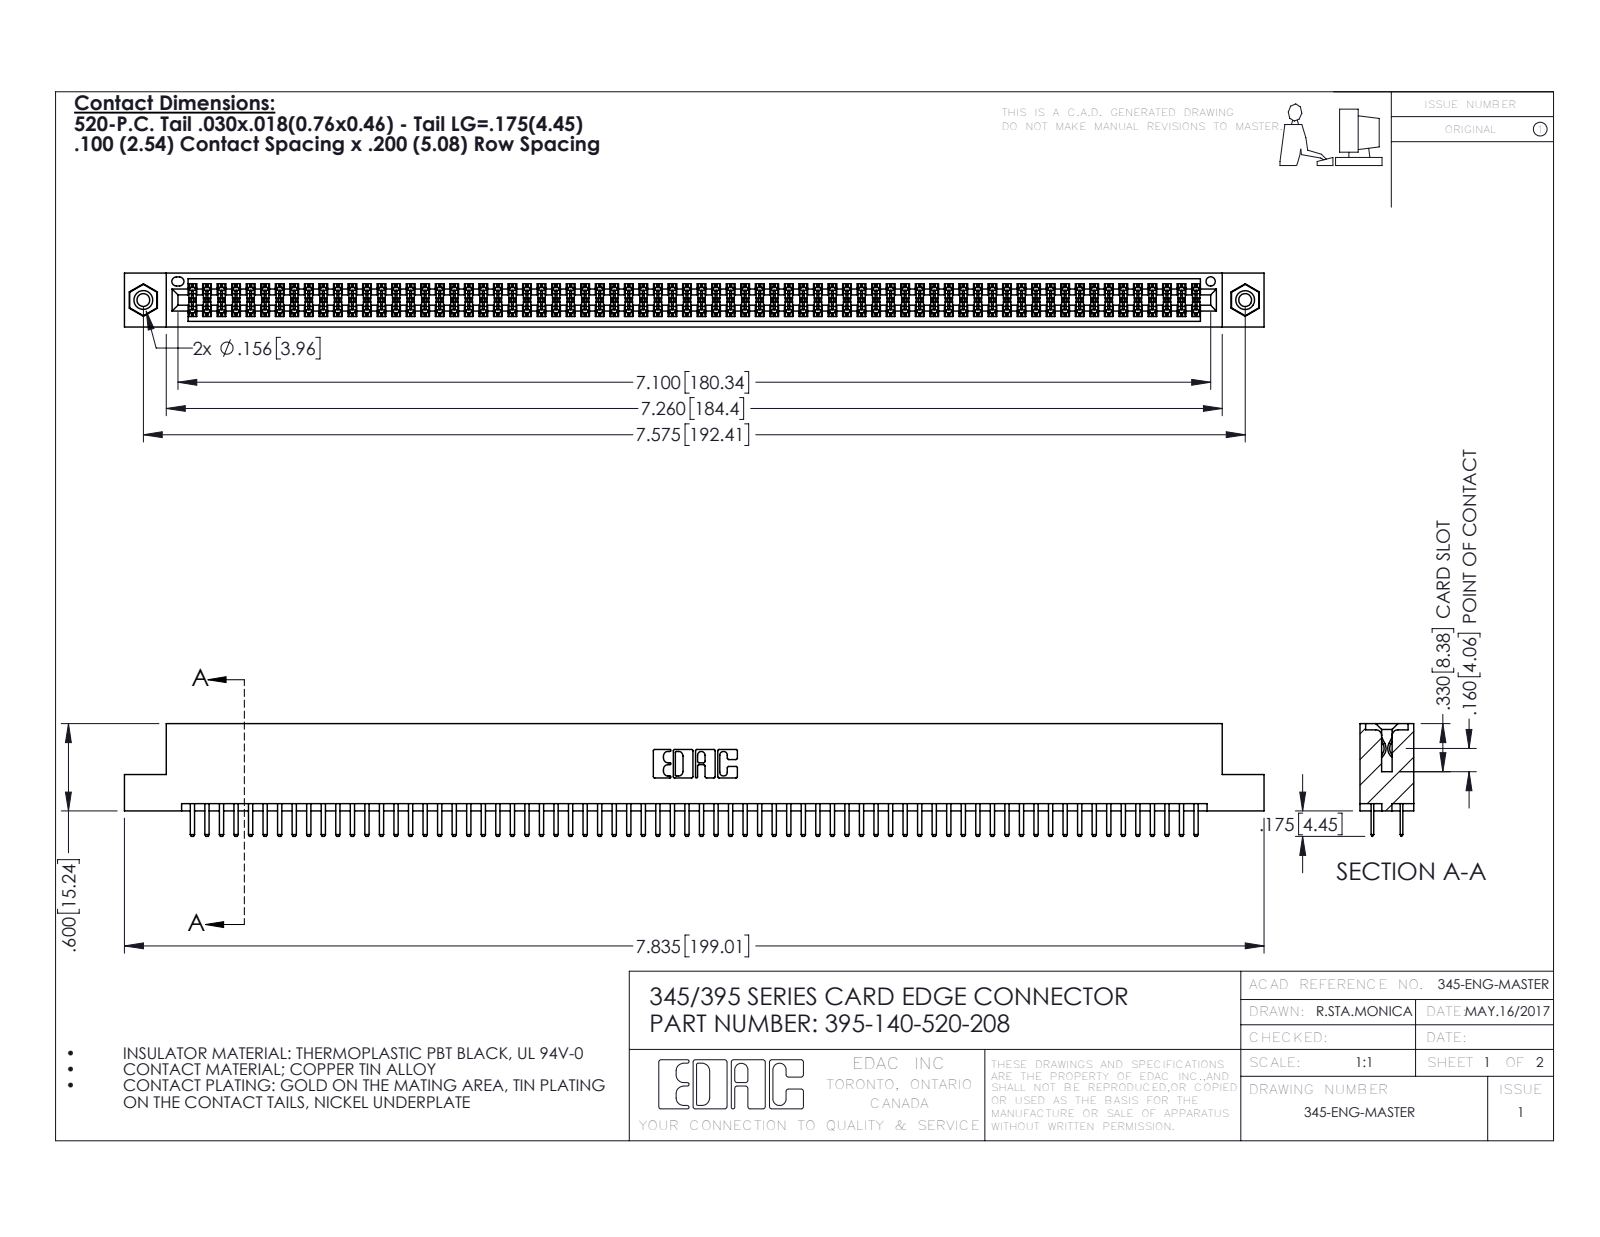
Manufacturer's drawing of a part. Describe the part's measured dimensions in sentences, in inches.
The part is named "395-140-520-208; 345-292-001_345-293-120; 345-250-001_345-250-003-102; 345 Part_Flush Mounting Lugs - 0.156 Dia-TI". Its 3-D file was written by "SolidWorks 2016 (CONFIG_CONTROL_DESIGN)". It is 143 solids with 7746 faces: 5012 planar, 2718 cylindrical and 16 other. Overall it measures 7.835 by 0.775 by 0.37 inches. Its volume is 1.191 cubic inches and its surface area 45.39 square inches. Round holes: 2 of diameter 0.089, 2 of diameter 0.125, 2 of diameter 0.156, 1 of diameter 0.064. Round bosses or shafts: 2 of diameter 0.155. Partial cylindrical surfaces (rounded edges, fillets, slot ends): 210 of radius 0.006, 144 of radius 0.01, 22 of radius 0.01, 6 of radius 0.007, 6 of radius 0.031, 3 of radius 0.026, 2 of radius 0.014, 2 of radius 0.019. The main face-to-face distances are 0.072, 0.298, 0.2, 0.37, 0.098, 0.272, 0.025, 0.225, 0.022, 0.072. The hole center spacings are 0.27, 7.339, 7.575.
